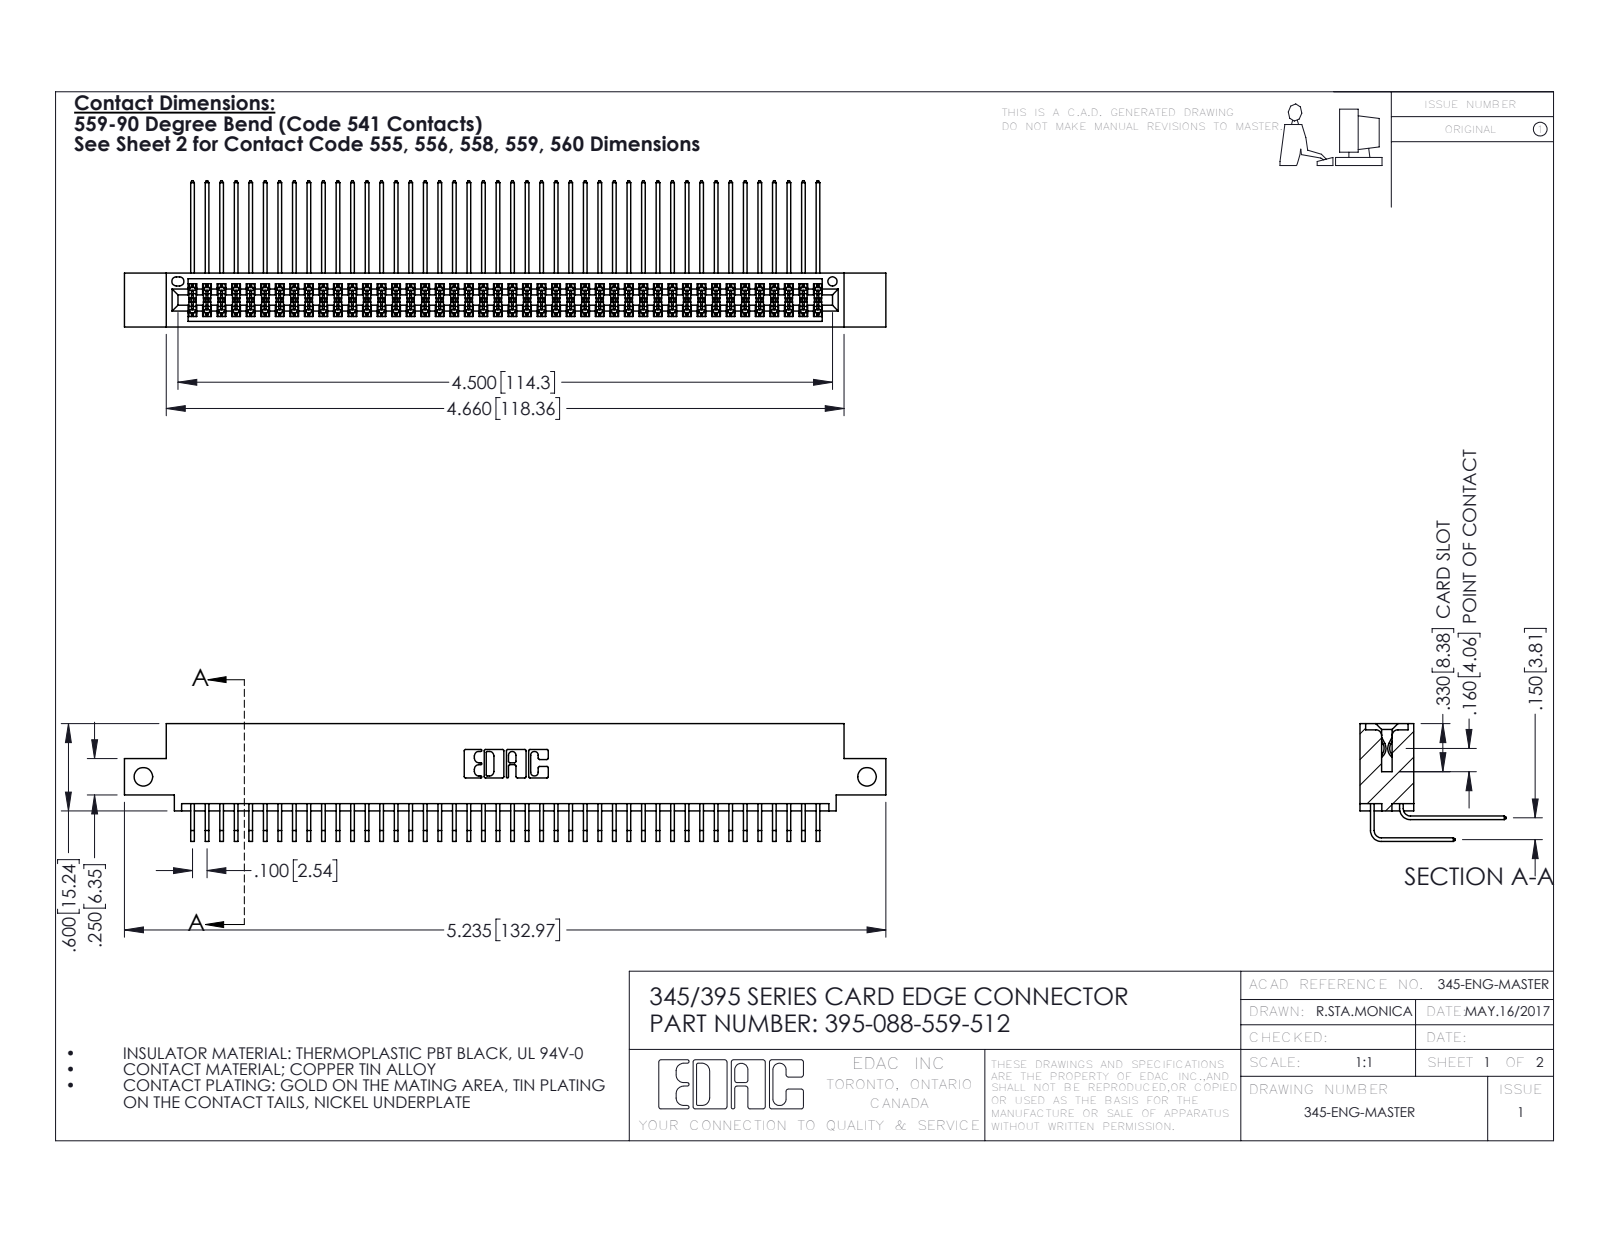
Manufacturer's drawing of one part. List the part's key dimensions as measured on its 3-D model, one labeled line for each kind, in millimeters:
Part name (STEP PRODUCT): 395-088-559-512; 345-292-001_559 Tail - 2; 345-292-001_558 559 Tail - 1; 345 Part_0.110 Offset - Side Mount
STEP written by: SolidWorks 2016 (CONFIG_CONTROL_DESIGN)
Units: millimetres
Bodies: 89 solids, 4706 faces (3164 planar, 1542 cylindrical, 0 other)
Overall size (bounding box): 133 × 25.5 × 20.5
Volume: 13 300 mm³ · Surface area: 22 020 mm²
Round holes (diameter × count): ⌀3.3 ×2, ⌀1.6 ×1
Partial cylindrical surfaces — rounded edges, fillets, slot ends (radius × count): R0.2 ×133, R0.3 ×22, R0.2 ×6, R0.8 ×6, R0.7 ×3, R0.4 ×2, R0.5 ×2, R0.6 ×2
Main face-to-face distances: 1.8, 7.6, 5.1, 9.4, 2.5, 6.9, 0.6, 5.7, 4.4, 3.8
Hole centre spacings: 126.4
